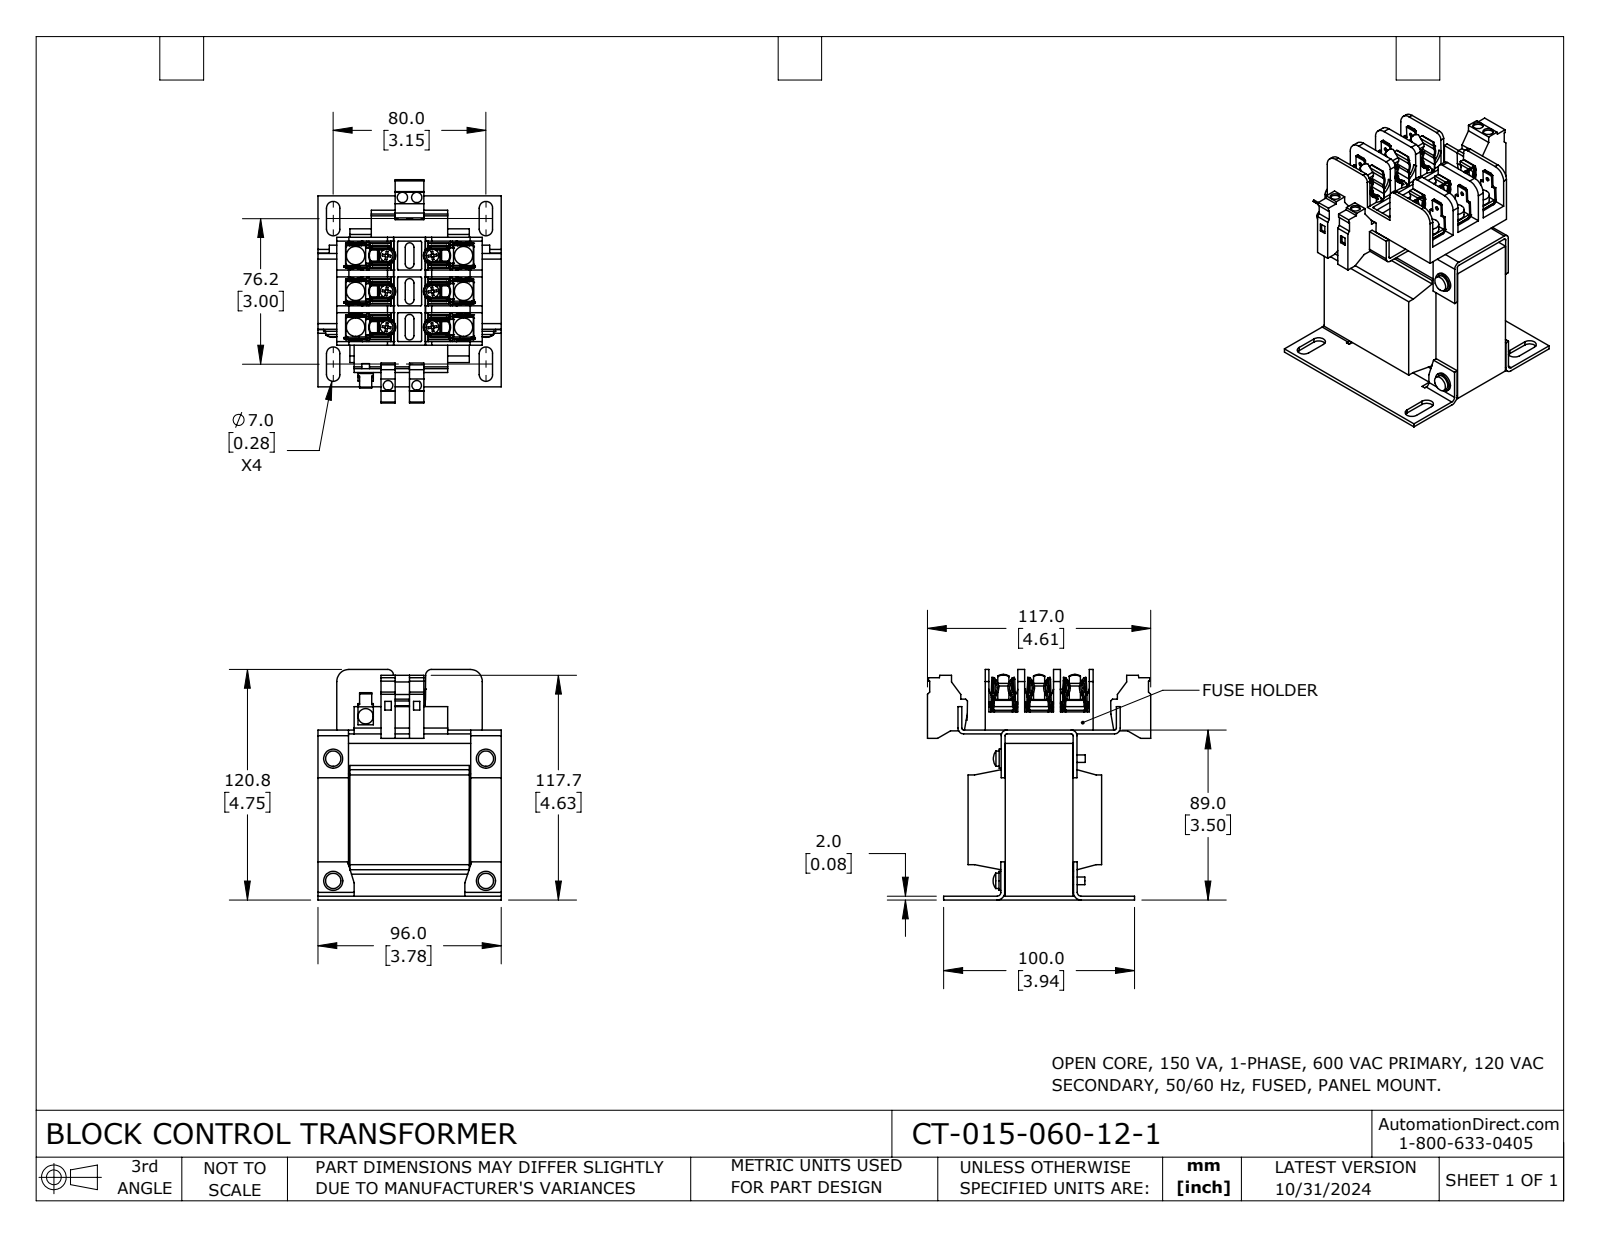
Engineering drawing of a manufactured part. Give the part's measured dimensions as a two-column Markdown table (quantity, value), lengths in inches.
| quantity | value |
| --- | --- |
| part name | CT-015-060-12-1 |
| STEP written by | SolidWorks 2023 (CONFIG_CONTROL_DESIGN) |
| units | inches |
| bodies | 2 solids, 1595 faces (1037 planar, 524 cylindrical, 34 other) |
| overall size | 4.754 × 4.606 × 3.78 |
| volume | 30 in³ |
| surface area | 194.1 in² |
| round holes (diameter × count) | 0.074 × 12, 0.205 × 5, 0.197 × 2, 0.213 × 2, 0.205 × 1 |
| round bosses / shafts (diameter × count) | 0.38 × 6, 0.19 × 6, 0.315 × 5, 0.157 × 5, 0.394 × 4, 0.177 × 4 |
| partial cylindrical surfaces (radius × count) | 0.01 × 24, 0.05 × 20, 0.03 × 18, 0.072 × 14, 0.038 × 12, 0.04 × 12, 0.164 × 12, 0.097 × 9 |
| main face-to-face distances | 0.079, 3.425, 3.504, 3.15, 0.657, 3.122, 0.63, 3.346, 0.738, 1.398 |
| hole center spacings | 2.232, 2.354, 0.026, 0.026, 0.052, 0.738, 2.345, 1.539 |
